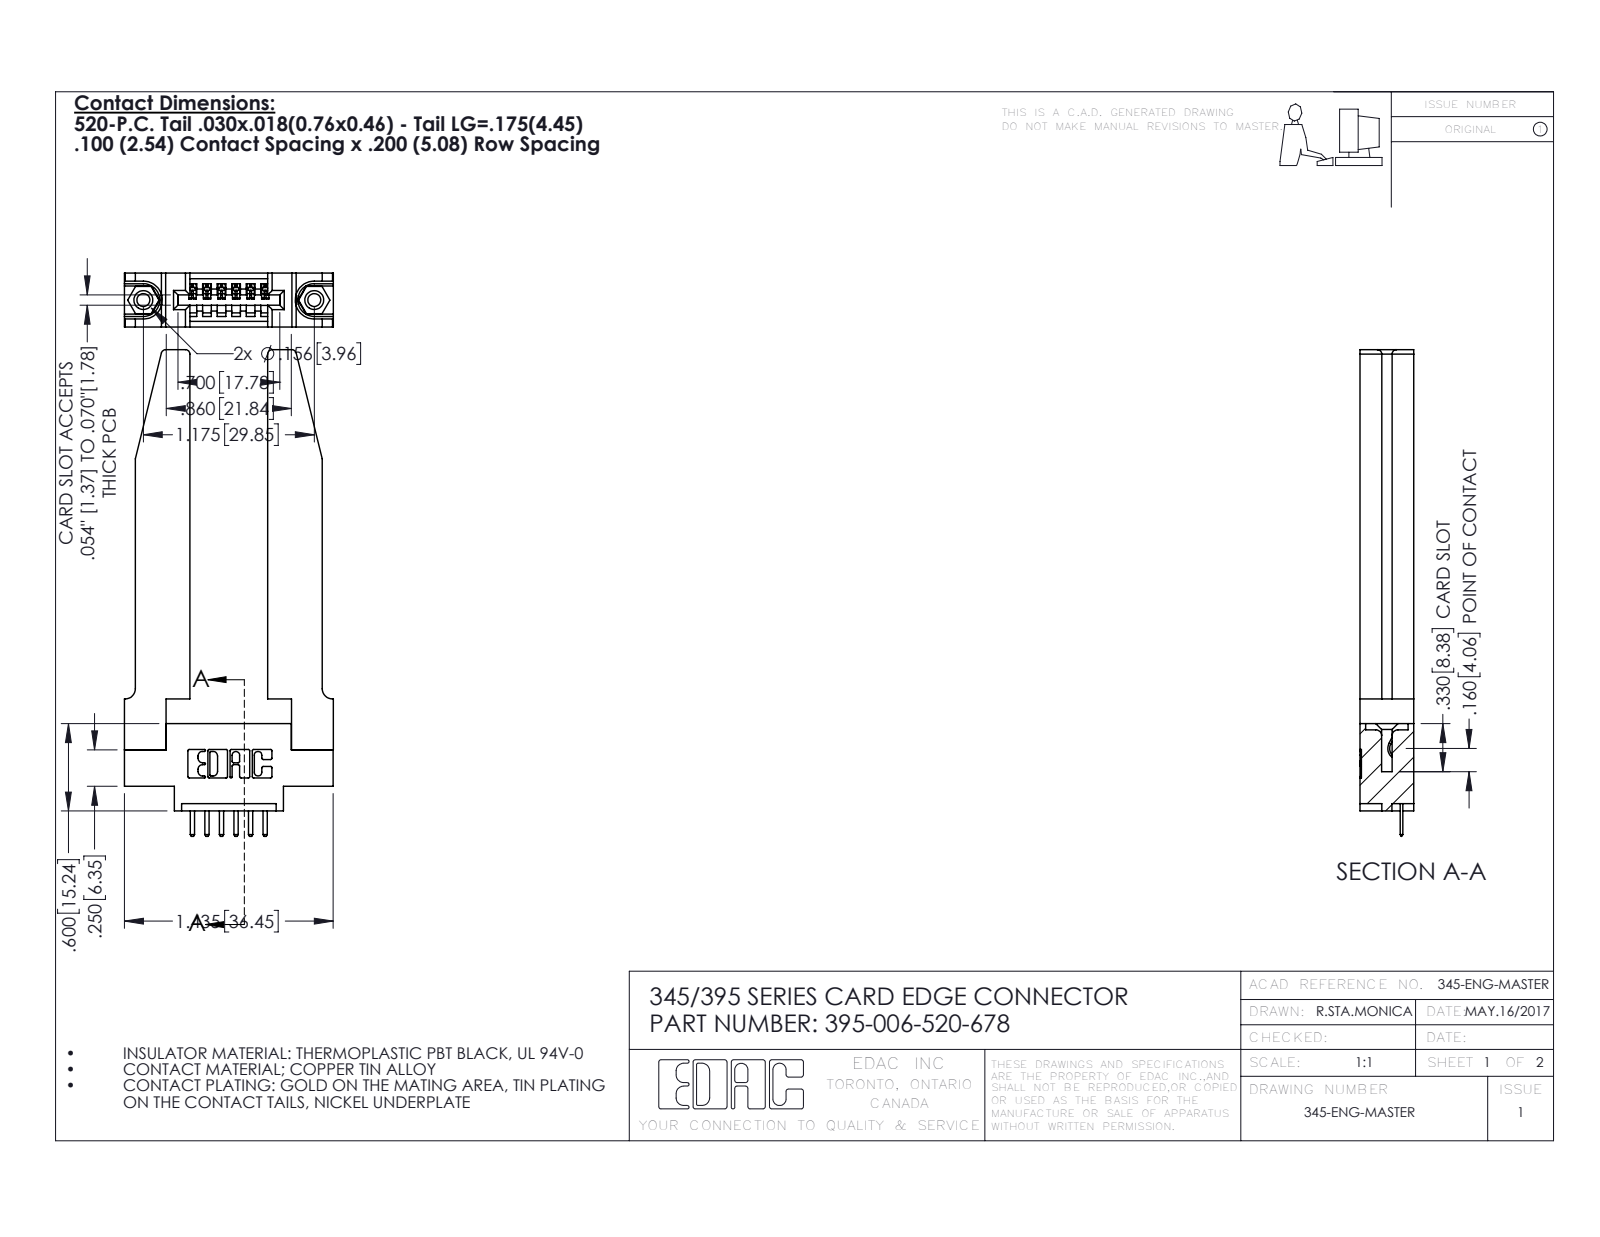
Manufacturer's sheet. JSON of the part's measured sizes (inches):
{"part_name": "395-006-520-678; 345-250-001_345-250-001-102; 345-292-001_345-293-120; 345-220-078_345-220-078 (+1 more)", "step_written_by": "SolidWorks 2016 (CONFIG_CONTROL_DESIGN)", "units": "inches", "bodies": {"solids": 11, "faces": 736, "planar": 478, "cylindrical": 206, "other": 52}, "overall_size": [3.345, 1.436, 0.37], "volume_in3": 0.66, "surface_area_in2": 16.22, "round_holes": [[0.089, 2], [0.125, 2], [0.156, 2], [0.064, 1]], "round_bosses_or_shafts": [[0.155, 2]], "partial_cylinders_radius": [[0.01, 22], [0.01, 14], [0.006, 12], [0.03, 8], [0.007, 6], [0.031, 6], [0.026, 3], [0.031, 2]], "face_to_face_distances": [0.37, 0.15, 0.22, 0.535, 0.072, 0.148, 0.298, 0.077, 0.095, 0.071], "hole_center_spacings": [0.27, 0.946, 1.175]}
